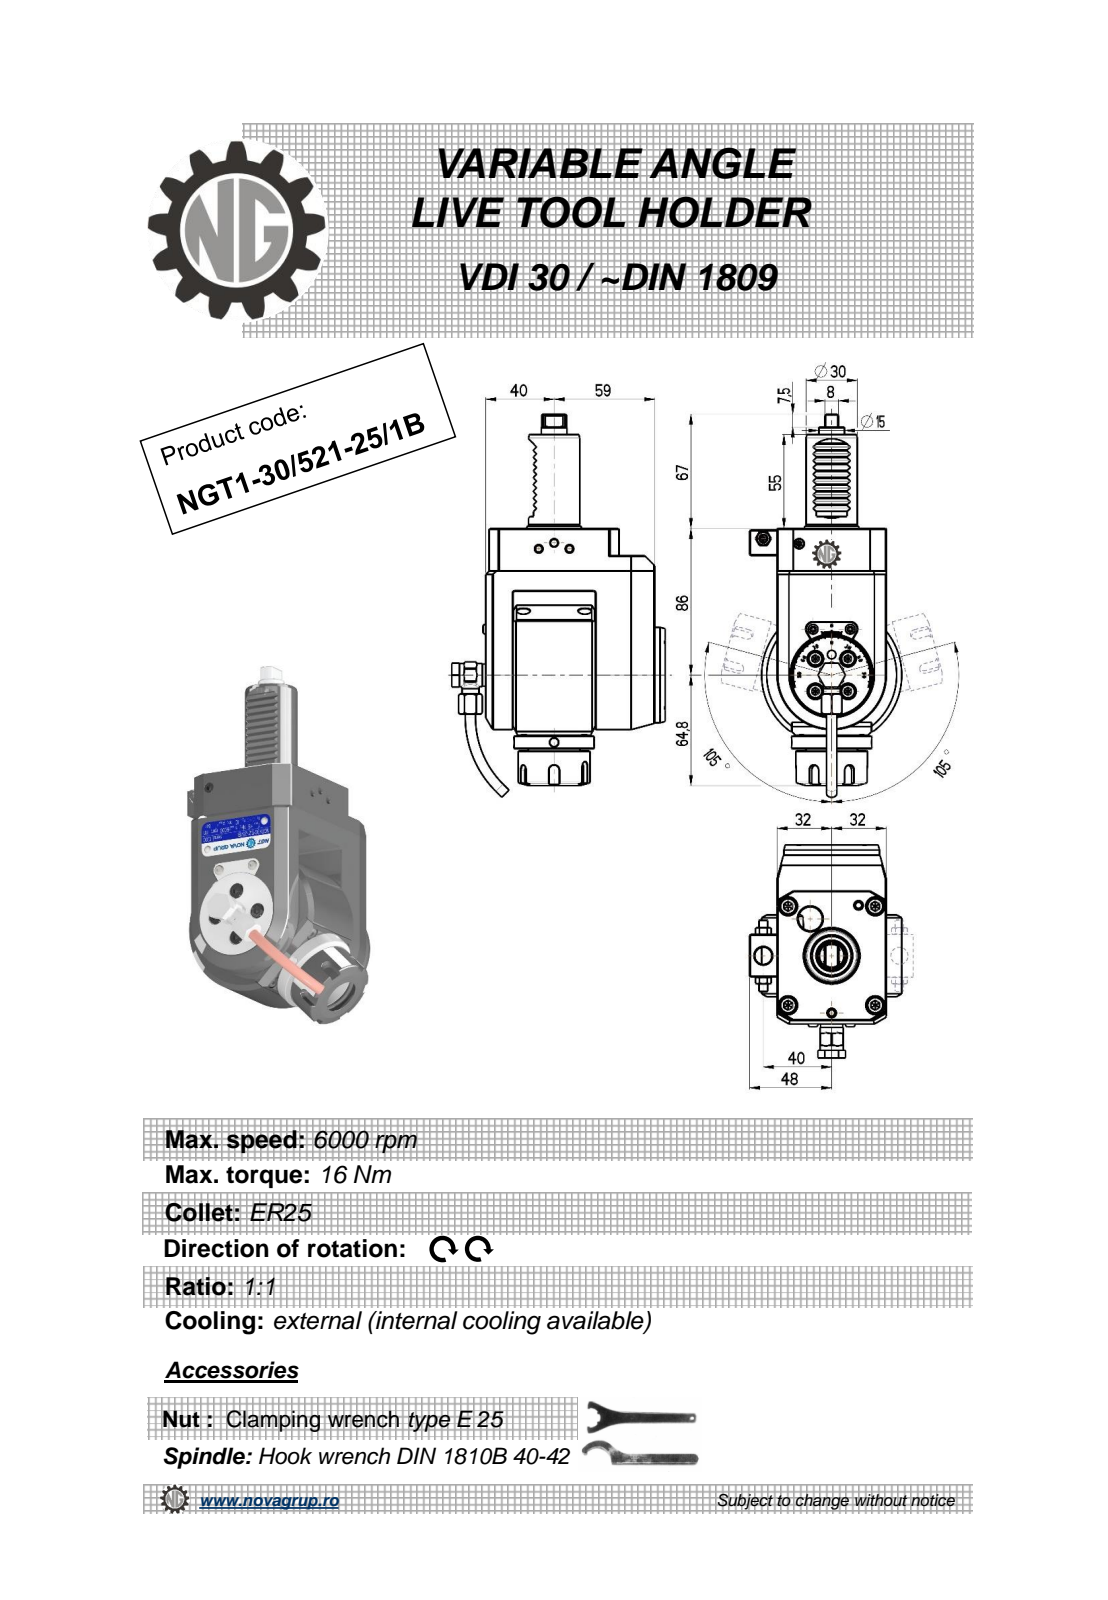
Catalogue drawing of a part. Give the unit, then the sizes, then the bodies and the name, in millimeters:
Units: millimetres
Overall size (bounding box): 224.67 × 124.9 × 89
Round holes (diameter × count): ⌀4 ×3, ⌀5 ×2, ⌀3 ×1, ⌀4.2 ×1, ⌀6.2 ×1, ⌀9 ×1, ⌀9.5 ×1, ⌀10 ×1, ⌀11 ×1, ⌀20.3 ×1
Round bosses / shafts (diameter × count): ⌀10 ×2, ⌀6 ×2, ⌀5.7 ×2, ⌀82 ×1, ⌀56 ×1, ⌀47 ×1, ⌀42 ×1, ⌀35 ×1
Partial cylindrical surfaces — rounded edges, fillets, slot ends (radius × count): R0.26 ×12, R0.3 ×10, R0.16 ×6, R3 ×5, R0.5 ×4, R0.8 ×2, R1 ×2, R7.2 ×1
Main face-to-face distances: 64, 16, 37, 6, 99, 105, 14, 21, 83, 35
Hole centre spacings: 0.4, 39.45, 40, 49, 49.4, 63.25, 63.56, 89.44
Volume: 786 164 mm³ · Surface area: 75 463 mm²
Bodies: 1 solid, 565 faces (239 planar, 138 cylindrical, 188 other)
Part name (STEP PRODUCT): NGT1_30_521_25_1B
STEP written by: PRO/ENGINEER BY PARAMETRIC TECHNOLOGY CORPORATION, 2010280 (CONFIG_CONTROL_DESIGN)
